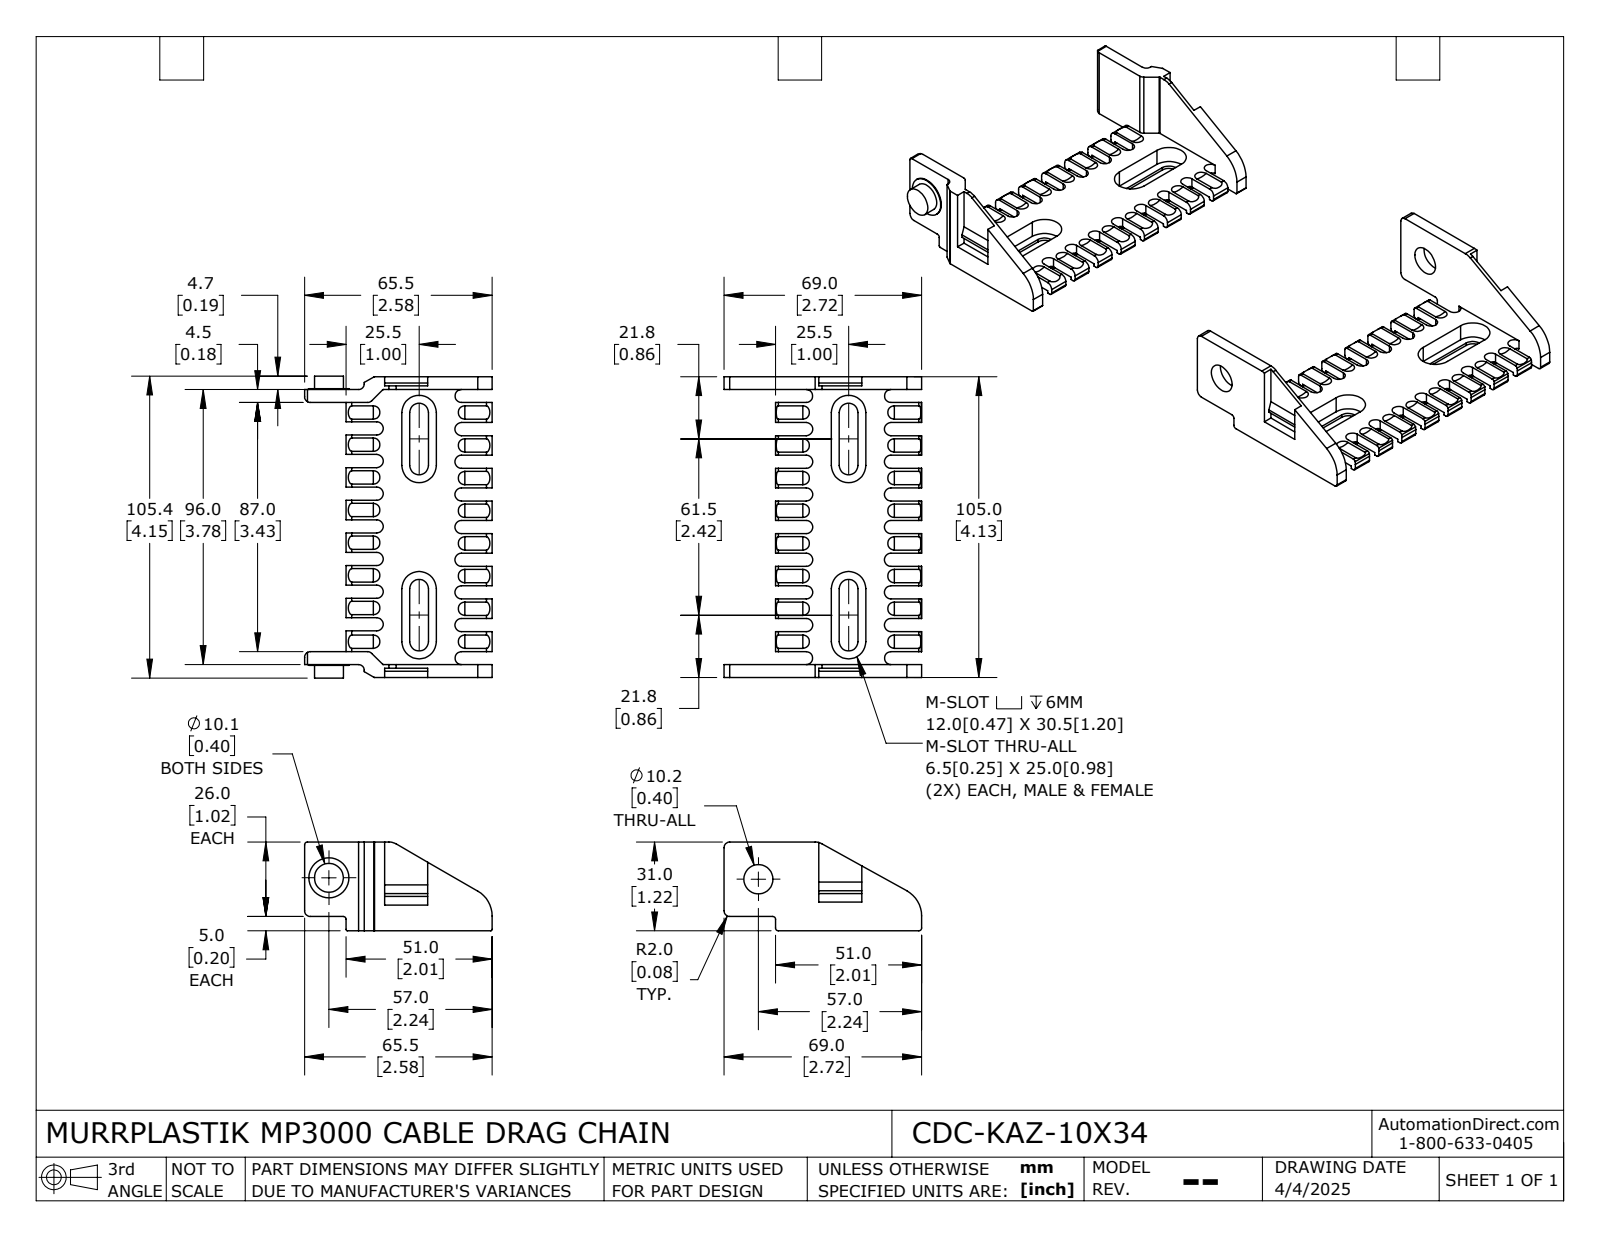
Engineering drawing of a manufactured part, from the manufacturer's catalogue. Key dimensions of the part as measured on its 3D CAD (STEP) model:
Part name (STEP PRODUCT): CDC-KAZ-10X34
STEP written by: SolidWorks 2024 (AUTOMOTIVE_DESIGN)
Units: millimetres
Bodies: 2 solids, 592 faces (306 planar, 254 cylindrical, 32 other)
Overall size (bounding box): 215.5 × 105.4 × 31
Volume: 62 644 mm³ · Surface area: 37 995 mm²
Round holes (diameter × count): ⌀10.2 ×1
Round bosses / shafts (diameter × count): ⌀14 ×1, ⌀10.1 ×1
Partial cylindrical surfaces — rounded edges, fillets, slot ends (radius × count): R2.3 ×28, R1 ×15, R7 ×14, R2 ×13, R3.25 ×8, R6 ×8, R2.25 ×6, R0.5 ×4
Main face-to-face distances: 4.5, 7, 100.5, 3.5, 96, 105, 9, 91.5, 2.5, 1
